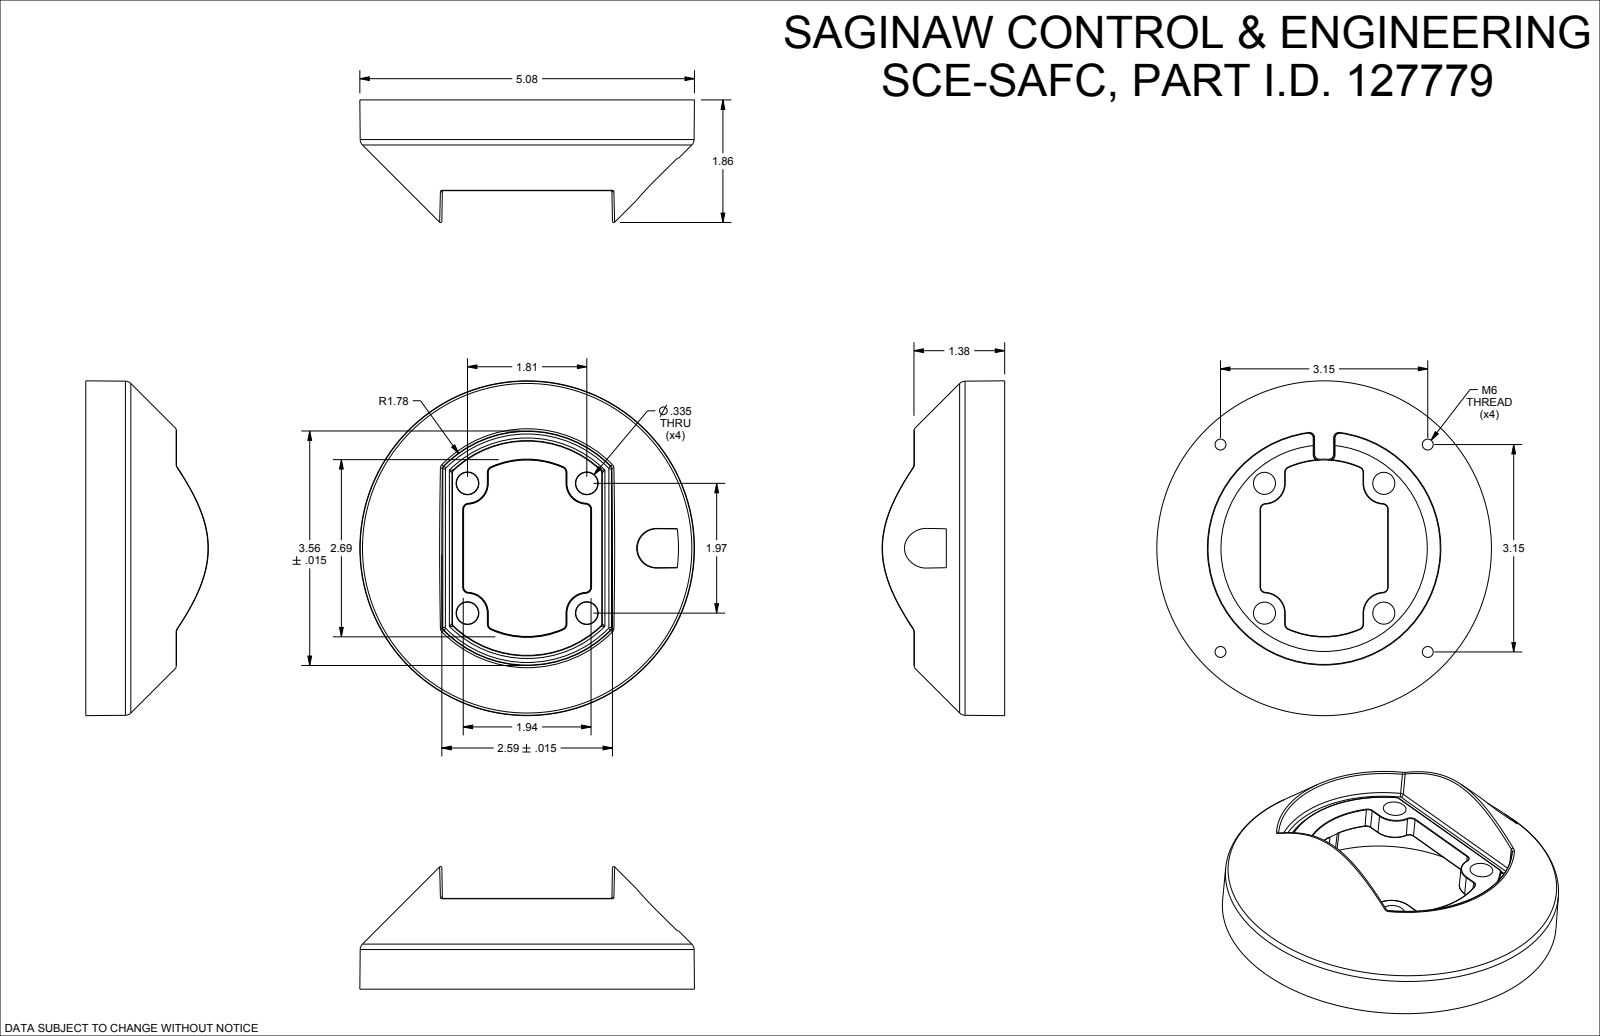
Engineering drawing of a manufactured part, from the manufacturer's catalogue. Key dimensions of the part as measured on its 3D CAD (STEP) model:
Part name (STEP PRODUCT): SCE-SAFC
STEP written by: SolidWorks 2023 (AUTOMOTIVE_DESIGN)
Units: inches
Bodies: 1 solid, 228 faces (23 planar, 24 cylindrical, 181 other)
Overall size (bounding box): 5.079 × 5.079 × 1.861
Volume: 10.58 in³ · Surface area: 83.04 in²
Round holes (diameter × count): ⌀0.165 ×4
Partial cylindrical surfaces — rounded edges, fillets, slot ends (radius × count): R0.008 ×12, R0.039 ×4
Main face-to-face distances: 0.709, 1.024, 0.315, 0.311, 0.965, 0.256, 0.059, 1.118, 0.807, 0.886
Hole centre spacings: 3.146, 4.449
